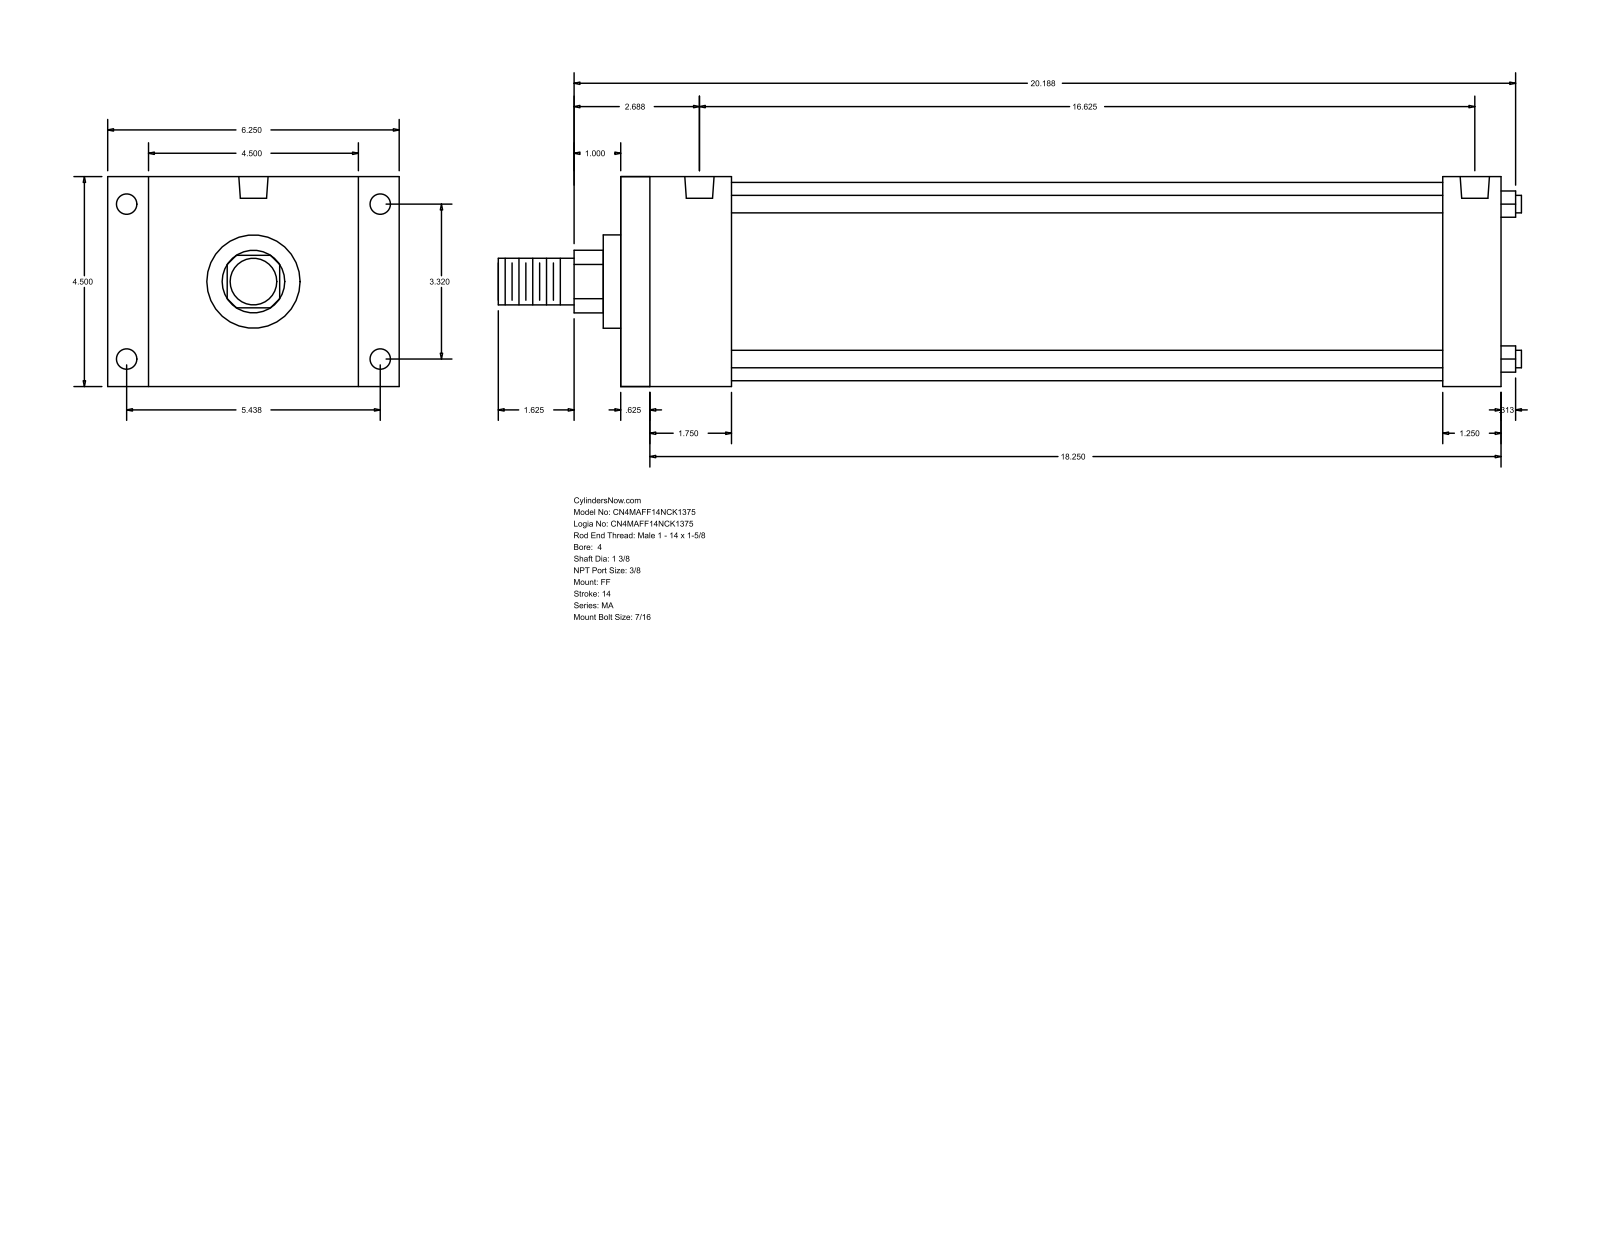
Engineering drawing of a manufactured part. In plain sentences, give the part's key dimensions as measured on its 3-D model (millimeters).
The part is named "MA_FF__0400_1.375". Its 3-D file was written by "GSSL Pune (CONFIG_CONTROL_DESIGN)". It is 0 solids with 92 faces: 64 planar, 28 cylindrical and 0 other. Overall it measures 557.21 by 158.75 by 114.3 millimeters. Round holes: 8 of diameter 11.11, 2 of diameter 15.93. Round bosses or shafts: 4 of diameter 9.53, 1 of diameter 107.95, 1 of diameter 50.8, 1 of diameter 34.92, 1 of diameter 25.4. Partial cylindrical surfaces (rounded edges, fillets, slot ends): 1 of radius 17.06. The main face-to-face distances are 114.3, 479.42, 15.87, 463.55, 22.23, 136.53, 447.67, 431.8, 31.75, 60.32. The hole center spacings are 4.77, 84.32, 138.12, 161.82, 412.74, 417.51, 422.28.
